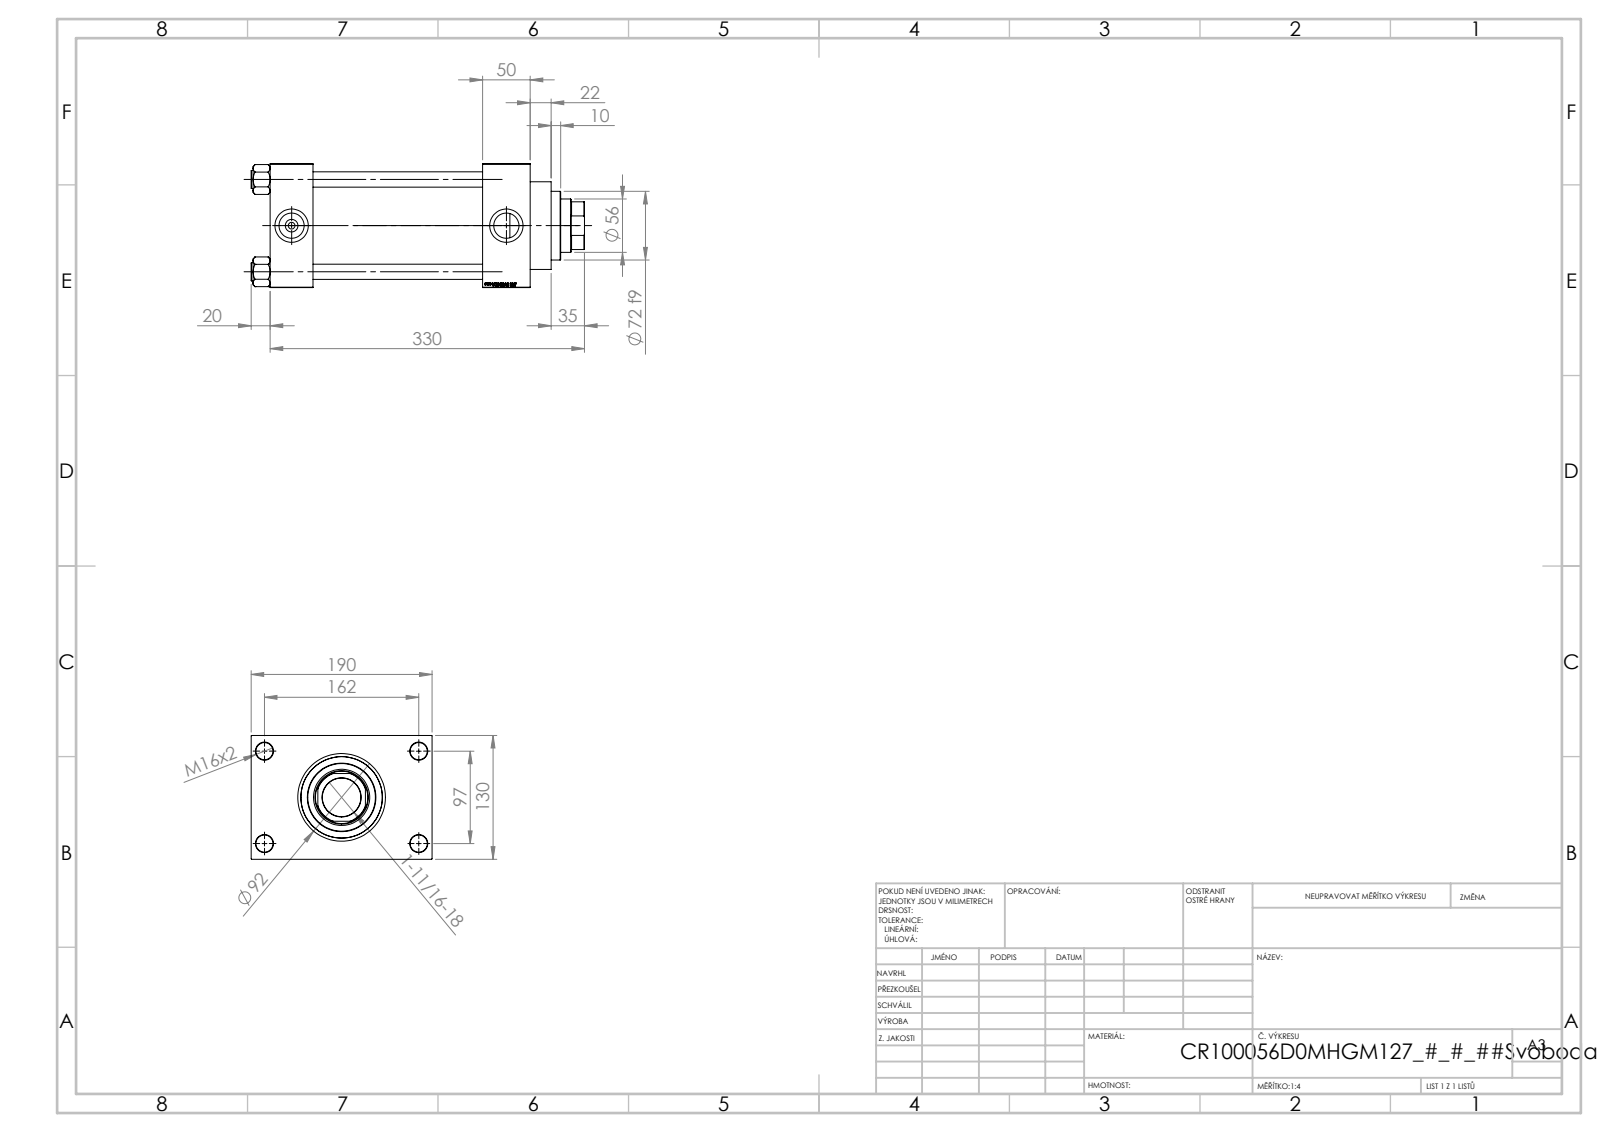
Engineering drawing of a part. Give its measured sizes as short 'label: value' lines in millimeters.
name: V215CR_VCP_D; V215CR_D_Body; V215_VC_A; NUT_M5_D (+1 more)
written by: SolidWorks 2019 (CONFIG_CONTROL_DESIGN)
unit: mm
bodies: 11 solids, 1151 faces (545 planar, 88 cylindrical, 518 other)
size: 350 × 190 × 130
volume: 3 082 000 mm³; area: 471 948 mm²
holes: 4× ⌀16, 4× ⌀18, 2× ⌀7, 2× ⌀26.44, 2× ⌀35, 1× ⌀40.5, 1× ⌀56, 1× ⌀59, 1× ⌀76, 1× ⌀85.5, 1× ⌀100
bosses: 4× ⌀19, 1× ⌀106, 1× ⌀92, 1× ⌀72
rounds: 1× R27
face distances: 130, 50, 45, 223, 178, 273, 228, 30, 160, 190
hole spacings: 32.55, 68.52, 94.41, 96.9, 102.27, 129.45, 161.73, 97
